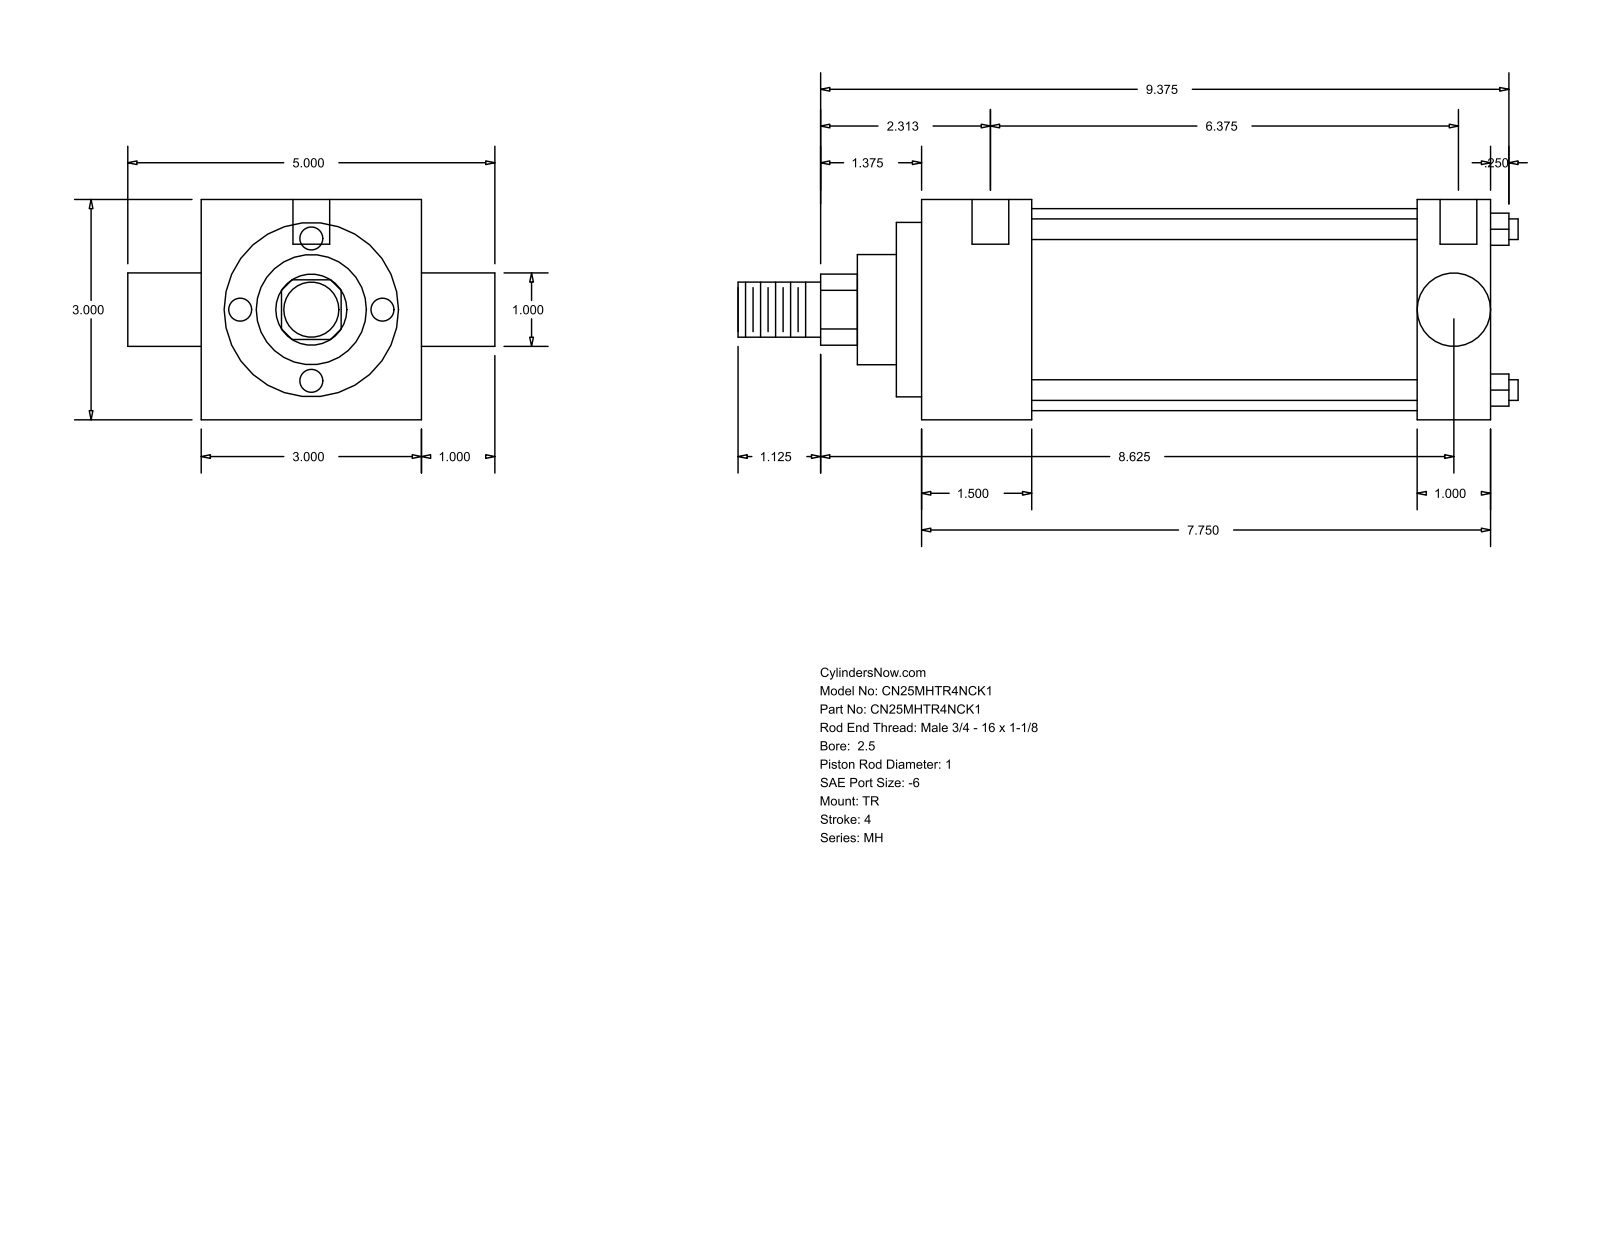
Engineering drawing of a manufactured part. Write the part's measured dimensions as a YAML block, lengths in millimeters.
part_name: "MH_TR__0250_1"
step_written_by: "GSSL Pune (CONFIG_CONTROL_DESIGN)"
units: millimeters
bodies: {solids: 0, faces: 86, planar: 61, cylindrical: 25, other: 0}
overall_size: [269.88, 127, 76.2]
round_holes:
  - {diameter: 5.56, count: 3}
  - {diameter: 12.7, count: 2}
round_bosses_or_shafts:
  - {diameter: 7.14, count: 4}
  - {diameter: 69.85, count: 1}
  - {diameter: 60.33, count: 1}
  - {diameter: 38.1, count: 1}
  - {diameter: 25.4, count: 1}
  - {diameter: 25.35, count: 1}
  - {diameter: 19.05, count: 1}
partial_cylinders:
  - {radius: 12.29, count: 1}
face_to_face_distances: [76.2, 196.86, 25.4, 38.11, 158.75, 171.46, 133.35, 8.73, 46.84, 180.19]
hole_center_spacings: [3.18, 4.76, 161.92, 165.1, 166.68, 169.86]
